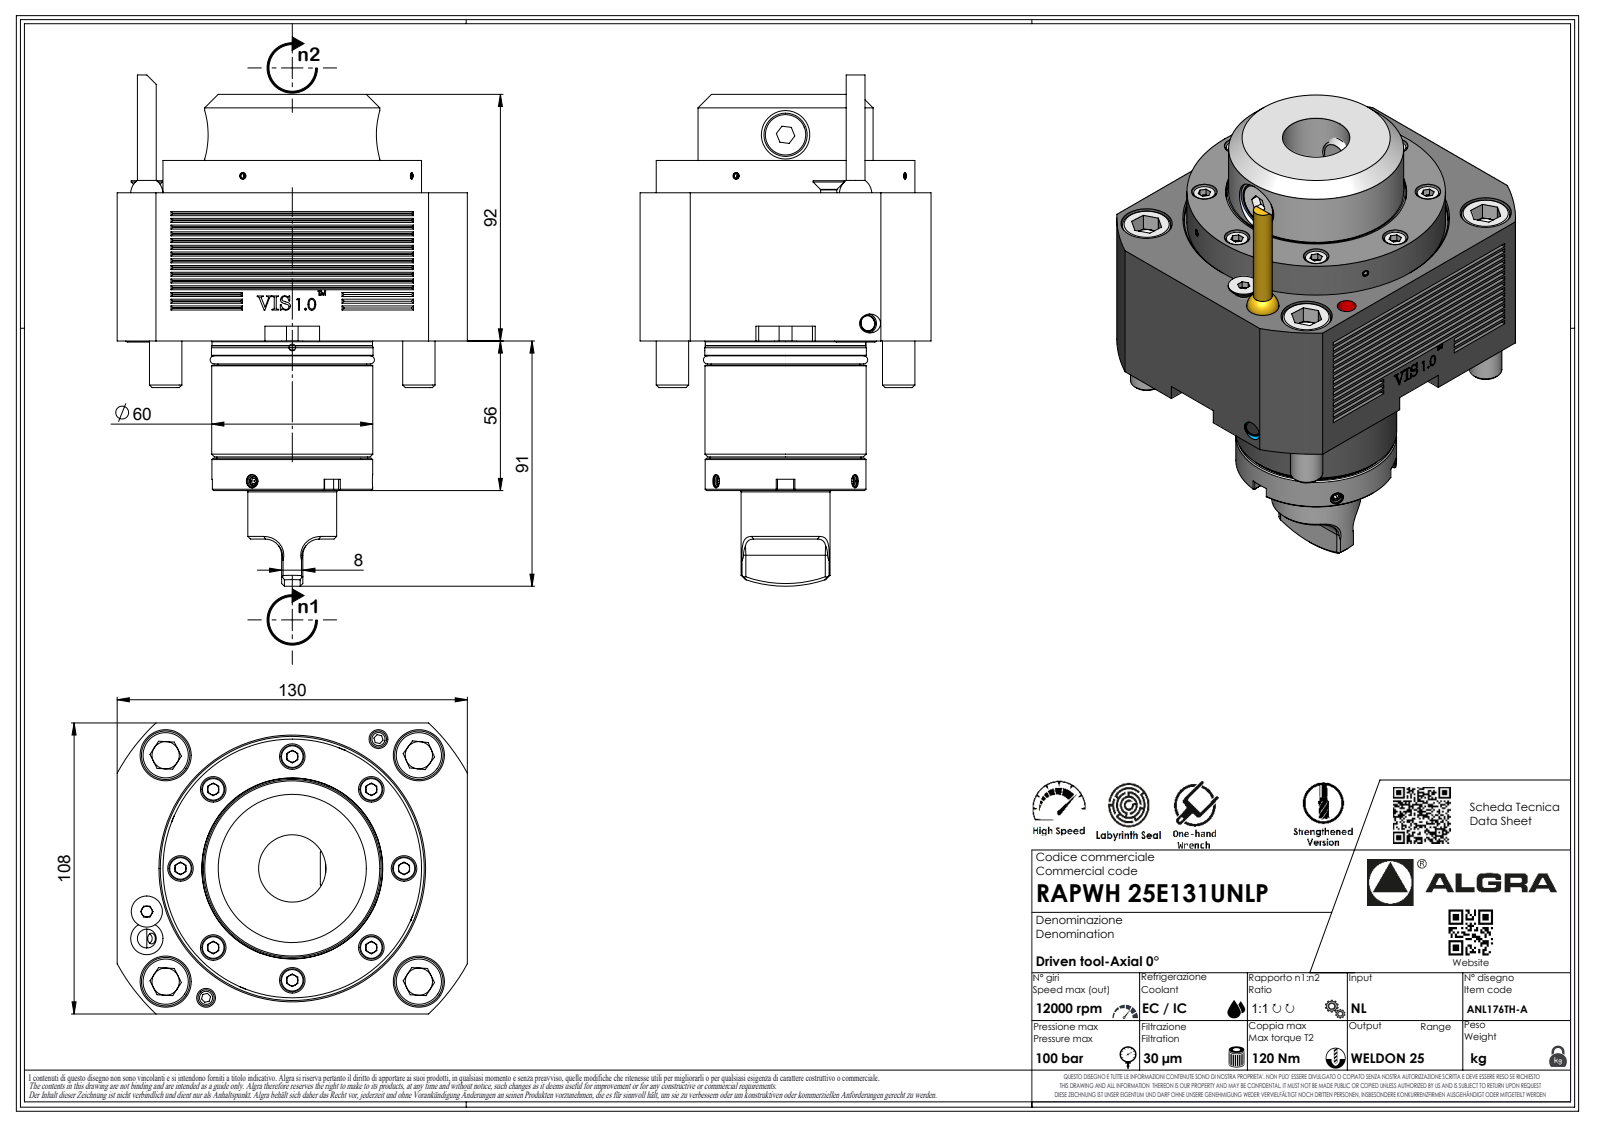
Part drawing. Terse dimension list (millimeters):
name: RAPWH25E131UNLP
written by: SolidWorks 2023 (AUTOMOTIVE_DESIGN)
unit: mm
bodies: 1 solid, 422 faces (275 planar, 58 cylindrical, 89 other)
size: 189.7 × 130 × 108
volume: 1 089 000 mm³; area: 77 054 mm²
holes: 1× ⌀2.1, 1× ⌀4
bosses: 4× ⌀12, 1× ⌀96, 1× ⌀65, 1× ⌀60, 1× ⌀59.6, 1× ⌀33, 1× ⌀7, 1× ⌀6.37
rounds: 8× R8, 7× R0.33, 7× R0.52, 7× R3.7, 6× R6, 1× R0.21, 1× R2, 1× R46
face distances: 55, 108, 67, 12, 130, 91.5, 36.5, 24.5, 55.5, 110.5
